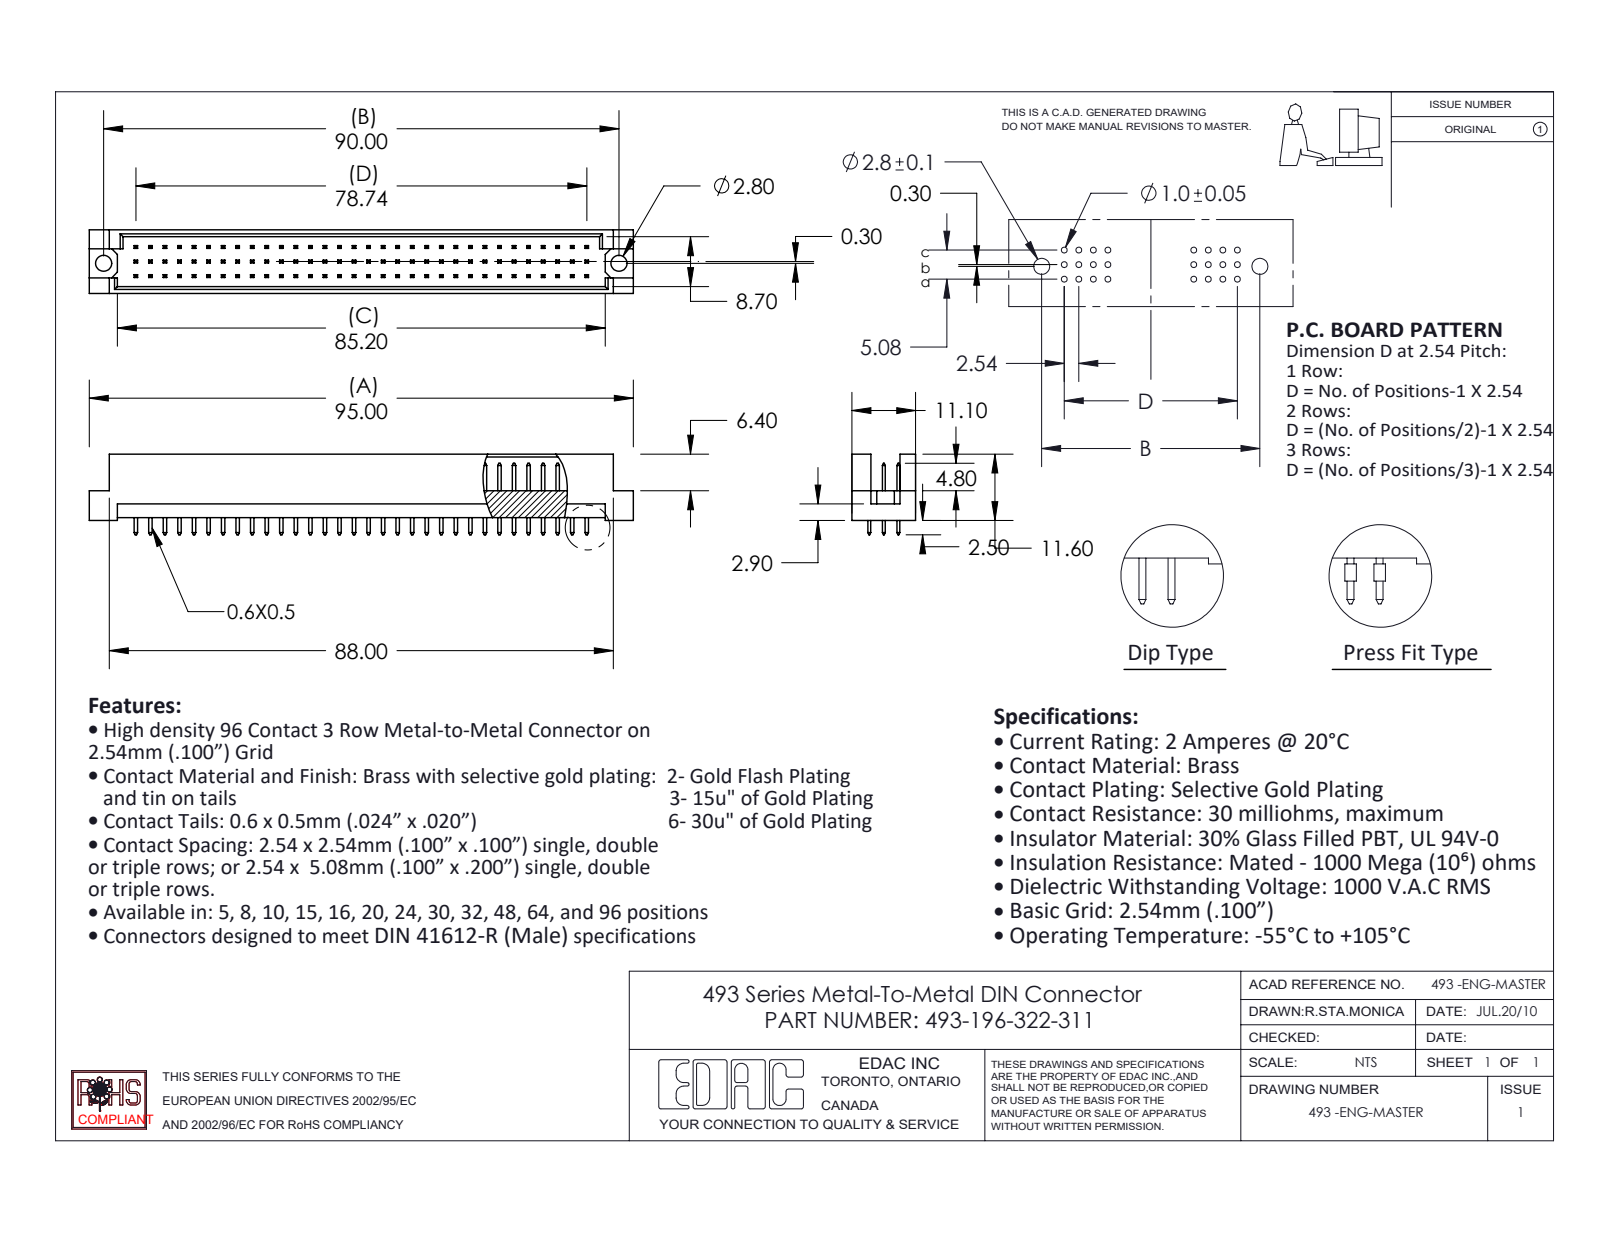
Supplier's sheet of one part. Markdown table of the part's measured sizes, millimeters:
| quantity | value |
| --- | --- |
| part name | 493 Part_96; 493-290_22; 493-196-322-311 |
| STEP written by | SolidWorks 2020 (CONFIG_CONTROL_DESIGN) |
| units | millimeters |
| bodies | 97 solids, 1780 faces (1776 planar, 4 cylindrical, 0 other) |
| overall size | 95 × 14.1 × 11.1 |
| volume | 6 008 mm³ |
| surface area | 9 077 mm² |
| round holes (diameter × count) | 2.8 × 2 |
| main face-to-face distances | 2.54, 1.2, 9.9, 0.5, 5.08, 11.1, 8.7, 4.7, 2.76, 3.26 |
| hole center spacings | 90 |
